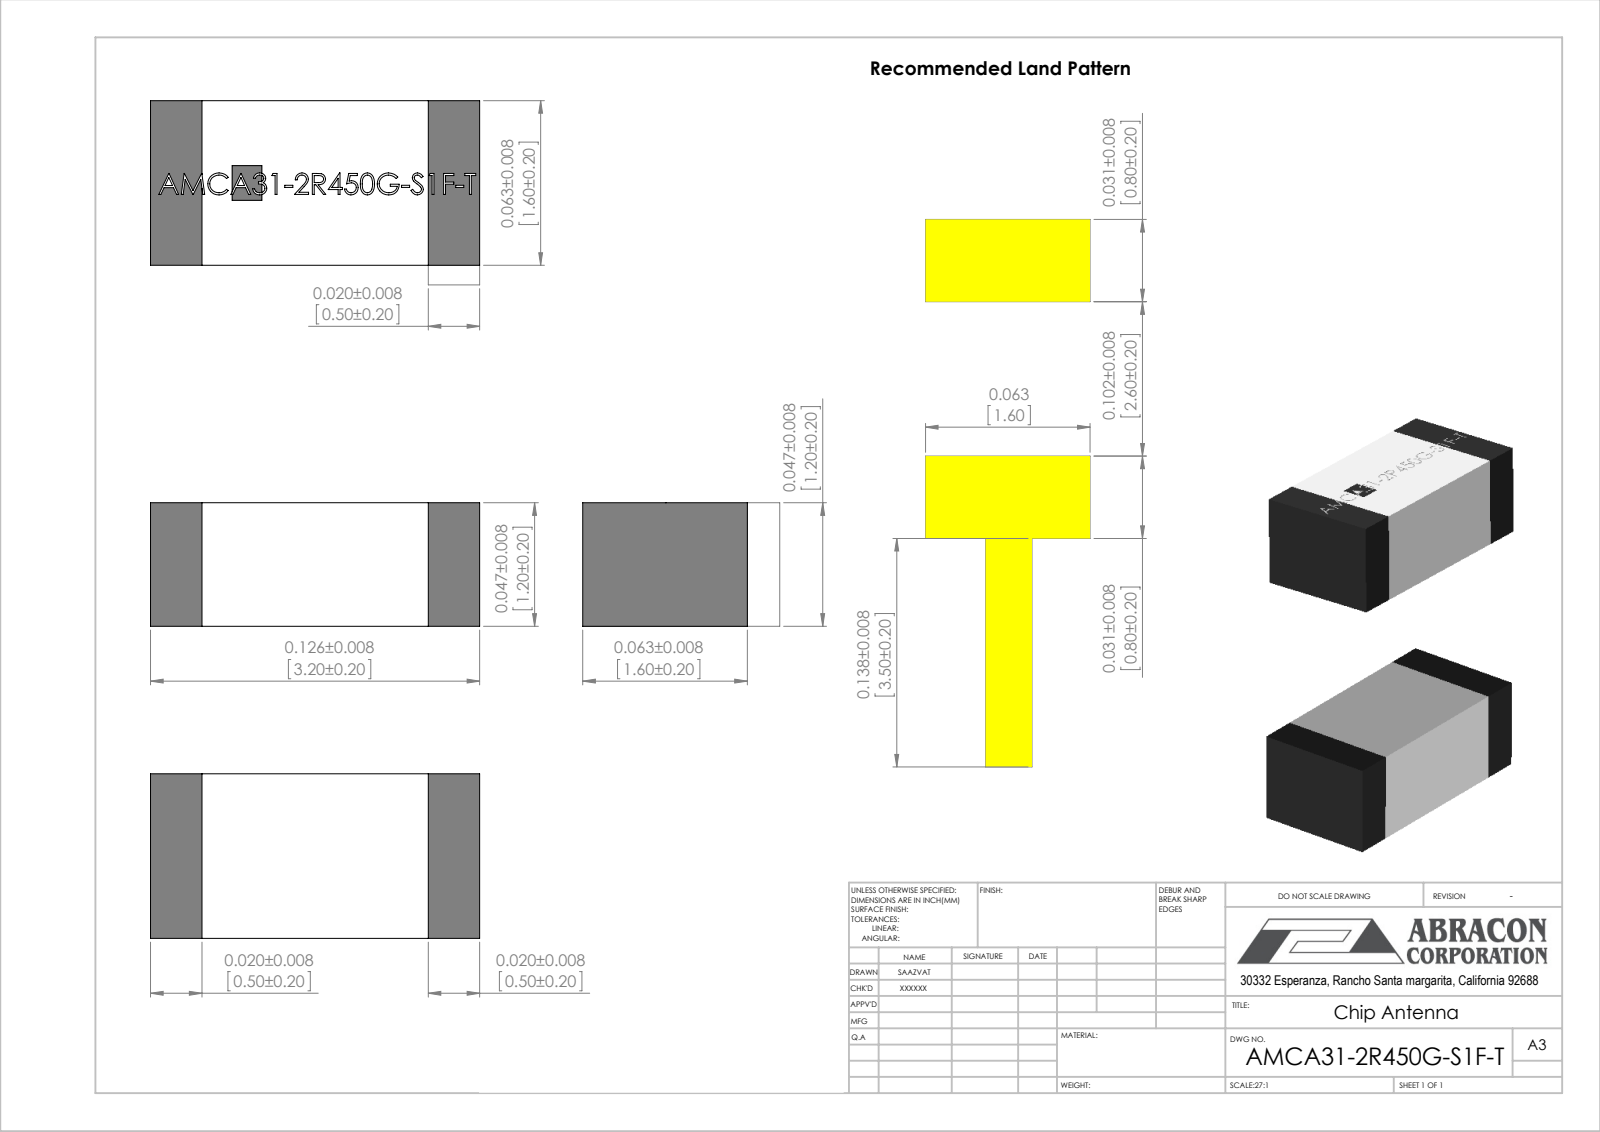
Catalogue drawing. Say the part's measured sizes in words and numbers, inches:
The part is named "AMCA31-2R450G-S1F-T". Its 3-D file was written by "SolidWorks 2012 (AUTOMOTIVE_DESIGN)". It is 1 solid with 240 faces: 165 planar, 0 cylindrical and 75 other. Overall it measures 0.126 by 0.063 by 0.047 inches. The main face-to-face distances are 0.047, 0.063, 0.126, 0.047, 0.025, 0.06, 0.014, 0.05, 0.028, 0.035.
